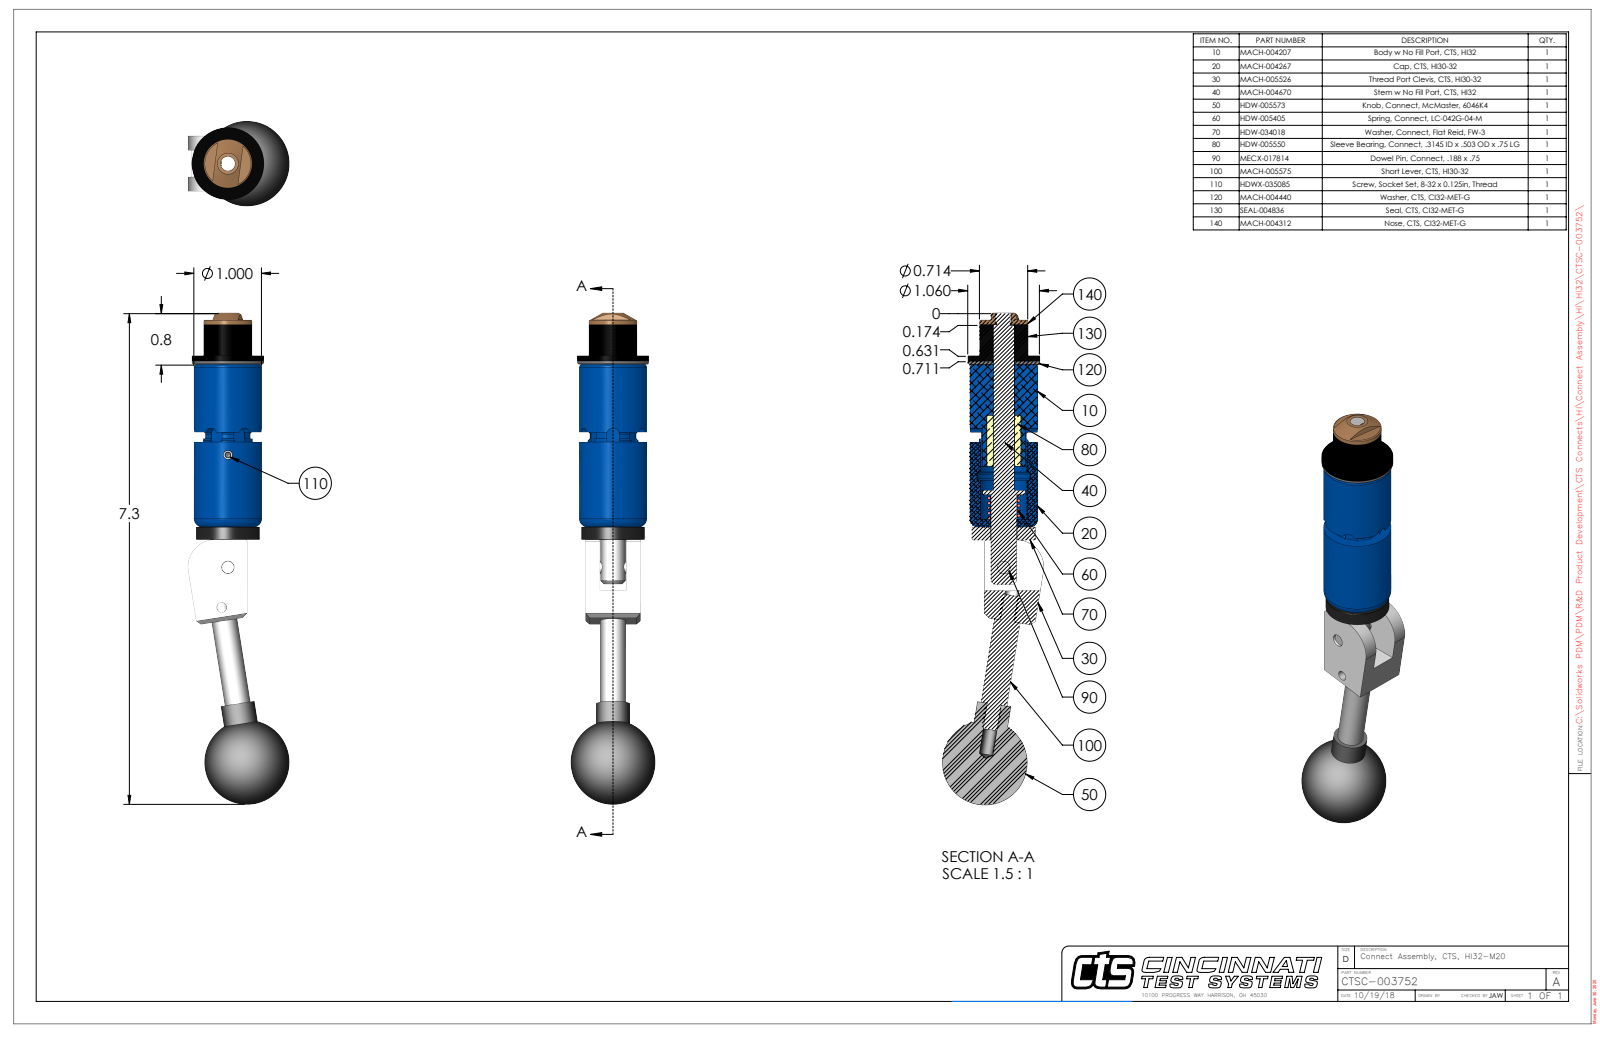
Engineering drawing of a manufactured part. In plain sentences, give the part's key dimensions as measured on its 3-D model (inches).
The part is named "CTSC-003752". Its 3-D file was written by "SolidWorks 2023 (AUTOMOTIVE_DESIGN)". It is 9 solids with 265 faces: 100 planar, 107 cylindrical and 58 other. Overall it measures 7.268 by 1.435 by 1.25 inches. Its volume is 4.037 cubic inches and its surface area 34.7 square inches. Round holes: 2 of diameter 0.201, 1 of diameter 0.136, 1 of diameter 0.15, 1 of diameter 0.189, 1 of diameter 0.213, 1 of diameter 0.31, 1 of diameter 0.314, 1 of diameter 0.316, 1 of diameter 0.385, 1 of diameter 0.392, 1 of diameter 0.688. Round bosses or shafts: 2 of diameter 0.25, 2 of diameter 0.201, 1 of diameter 1.06, 1 of diameter 1, 1 of diameter 0.936, 1 of diameter 0.714, 1 of diameter 0.5, 1 of diameter 0.38. Partial cylindrical surfaces (rounded edges, fillets, slot ends): 6 of radius 0.093, 2 of radius 0.029, 1 of radius 0.375, 1 of radius 0.4, 1 of radius 0.458. The main face-to-face distances are 0.05, 0.21, 0.602, 2.448, 2.398, 0.812, 0.537, 0.587, 2.985, 3.172. The hole center spacings are 0.599, 1.658, 2.252.
